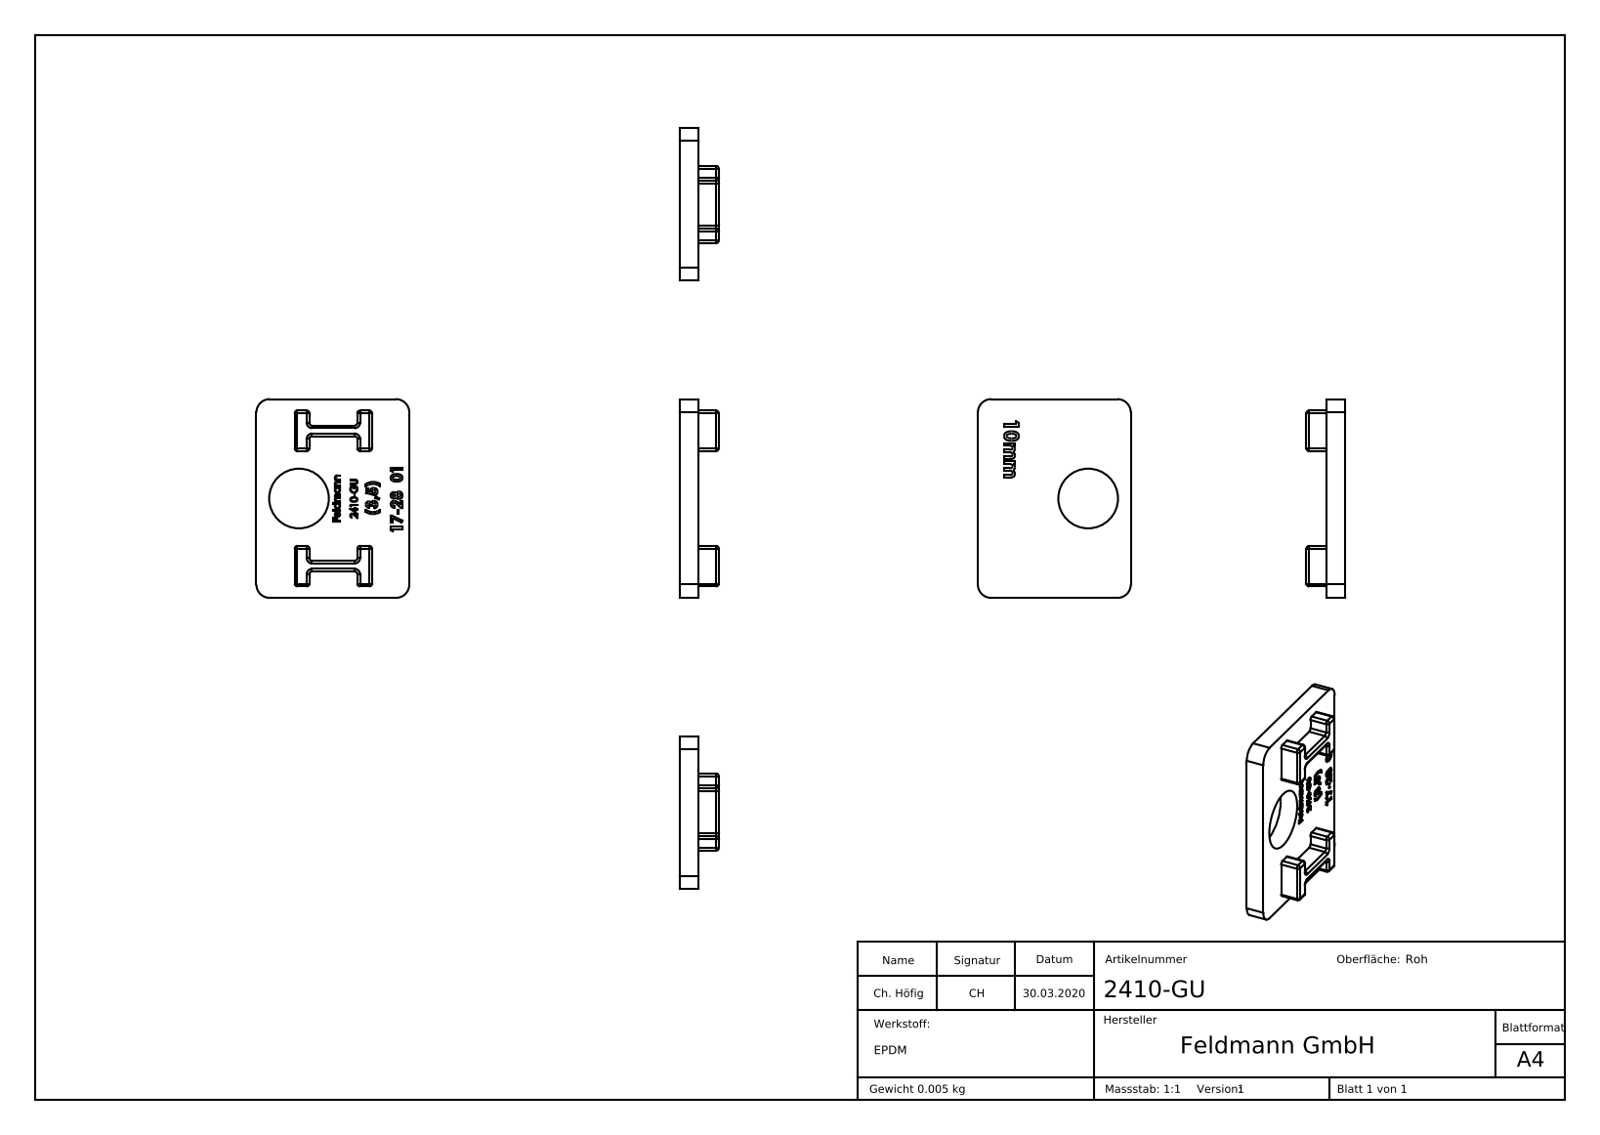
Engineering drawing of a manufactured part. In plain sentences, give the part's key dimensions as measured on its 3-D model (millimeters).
The part is named "2410-GU". Its 3-D file was written by "SolidWorks 2018 (CONFIG_CONTROL_DESIGN)". It is 1 solid with 486 faces: 241 planar, 53 cylindrical and 192 other. Overall it measures 37.3 by 28.7 by 7.3 millimeters. Its volume is 3 827 cubic millimeters and its surface area 2 904 square millimeters. Round holes: 1 of diameter 11.2. Partial cylindrical surfaces (rounded edges, fillets, slot ends): 36 of radius 0.5, 4 of radius 2.5. The main face-to-face distances are 3.5, 28.7, 37.3, 25.4, 7.3, 3.8, 7.2, 2, 6.95, 4.95.
